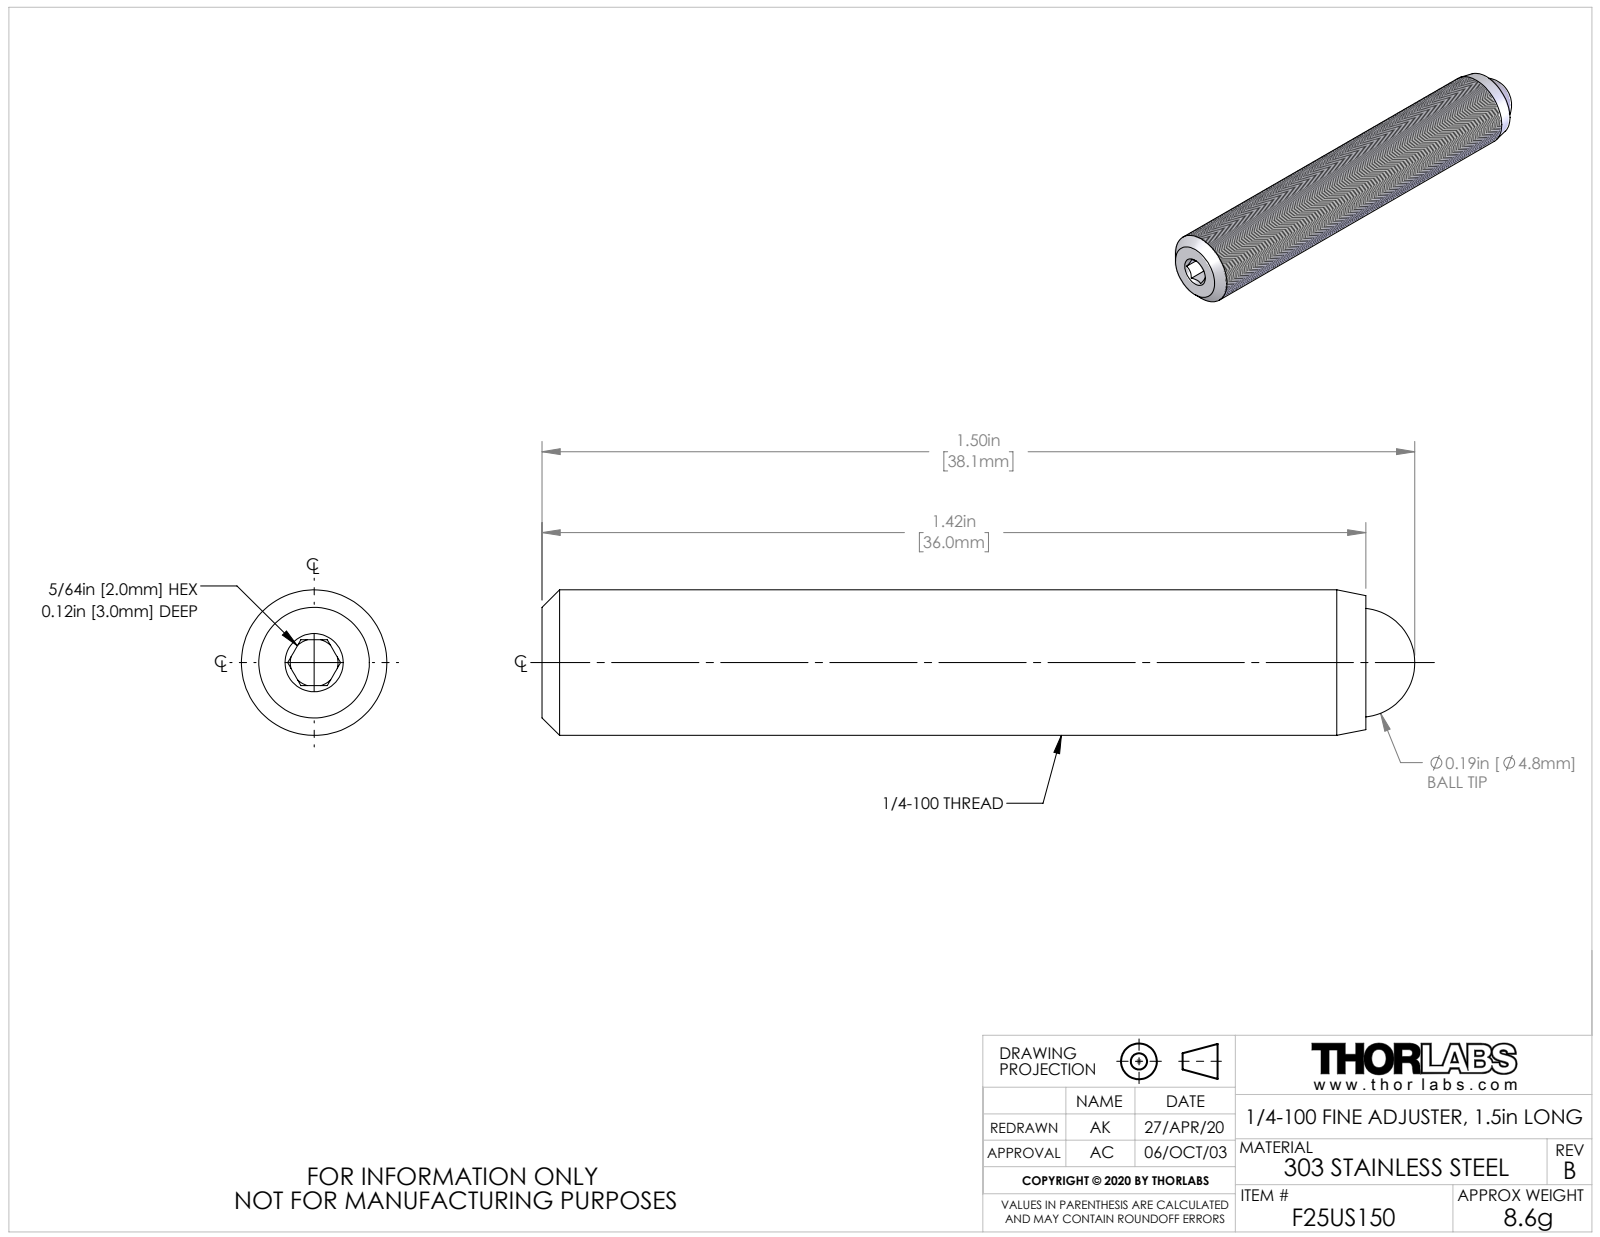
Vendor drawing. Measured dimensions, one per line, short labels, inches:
name: 7645-E0W
written by: SolidWorks 2018 (AUTOMOTIVE_DESIGN)
unit: in
bodies: 2 solids, 38 faces (20 planar, 6 cylindrical, 12 other)
size: 1.5 × 0.25 × 0.25
volume: 0.069 in³; area: 1.379 in²
holes: 1× ⌀0.082, 1× ⌀0.188
bosses: 1× ⌀0.25
face distances: 0.079, 1.416, 1.296, 0.12
